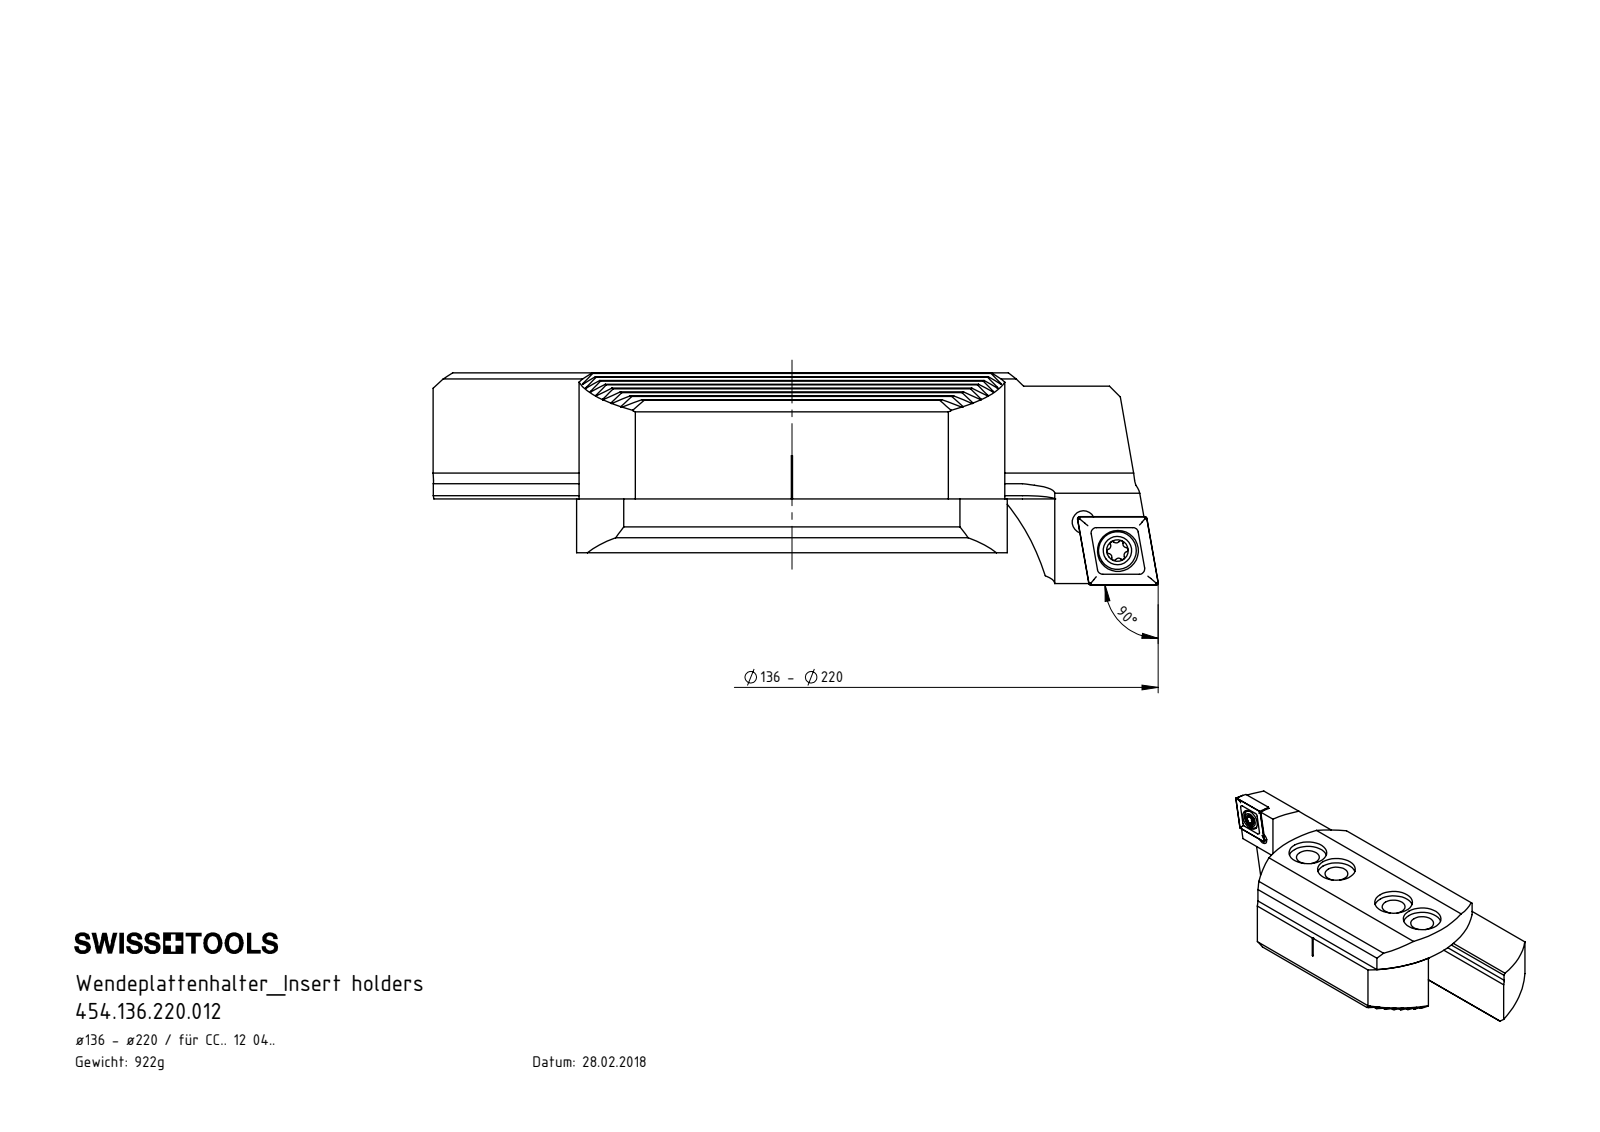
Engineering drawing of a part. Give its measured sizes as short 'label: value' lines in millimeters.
name: F00-WCB.136.003_A; CCMT120404; 454.136.220.012; WCC-ER2.001.010_A (+3 more)
written by: SolidWorks 2017 (CONFIG_CONTROL_DESIGN)
unit: mm
bodies: 5 solids, 632 faces (382 planar, 68 cylindrical, 182 other)
size: 134.59 × 55 × 39.4
volume: 117 488 mm³; area: 32 184 mm²
holes: 4× ⌀8.5, 4× ⌀14, 2× ⌀4.2, 1× ⌀5.5, 1× ⌀7.6
bosses: 1× ⌀7, 1× ⌀5
rounds: 16× R0.2, 6× R0.39, 6× R40, 3× R0.69, 3× R0.69, 1× R0.8, 1× R6
face distances: 2.38, 4.76, 21.3, 33.7, 7.14, 12.4, 9.52, 10, 4.77, 7.15
hole spacings: 15, 45, 8.21, 8.33, 30, 60
